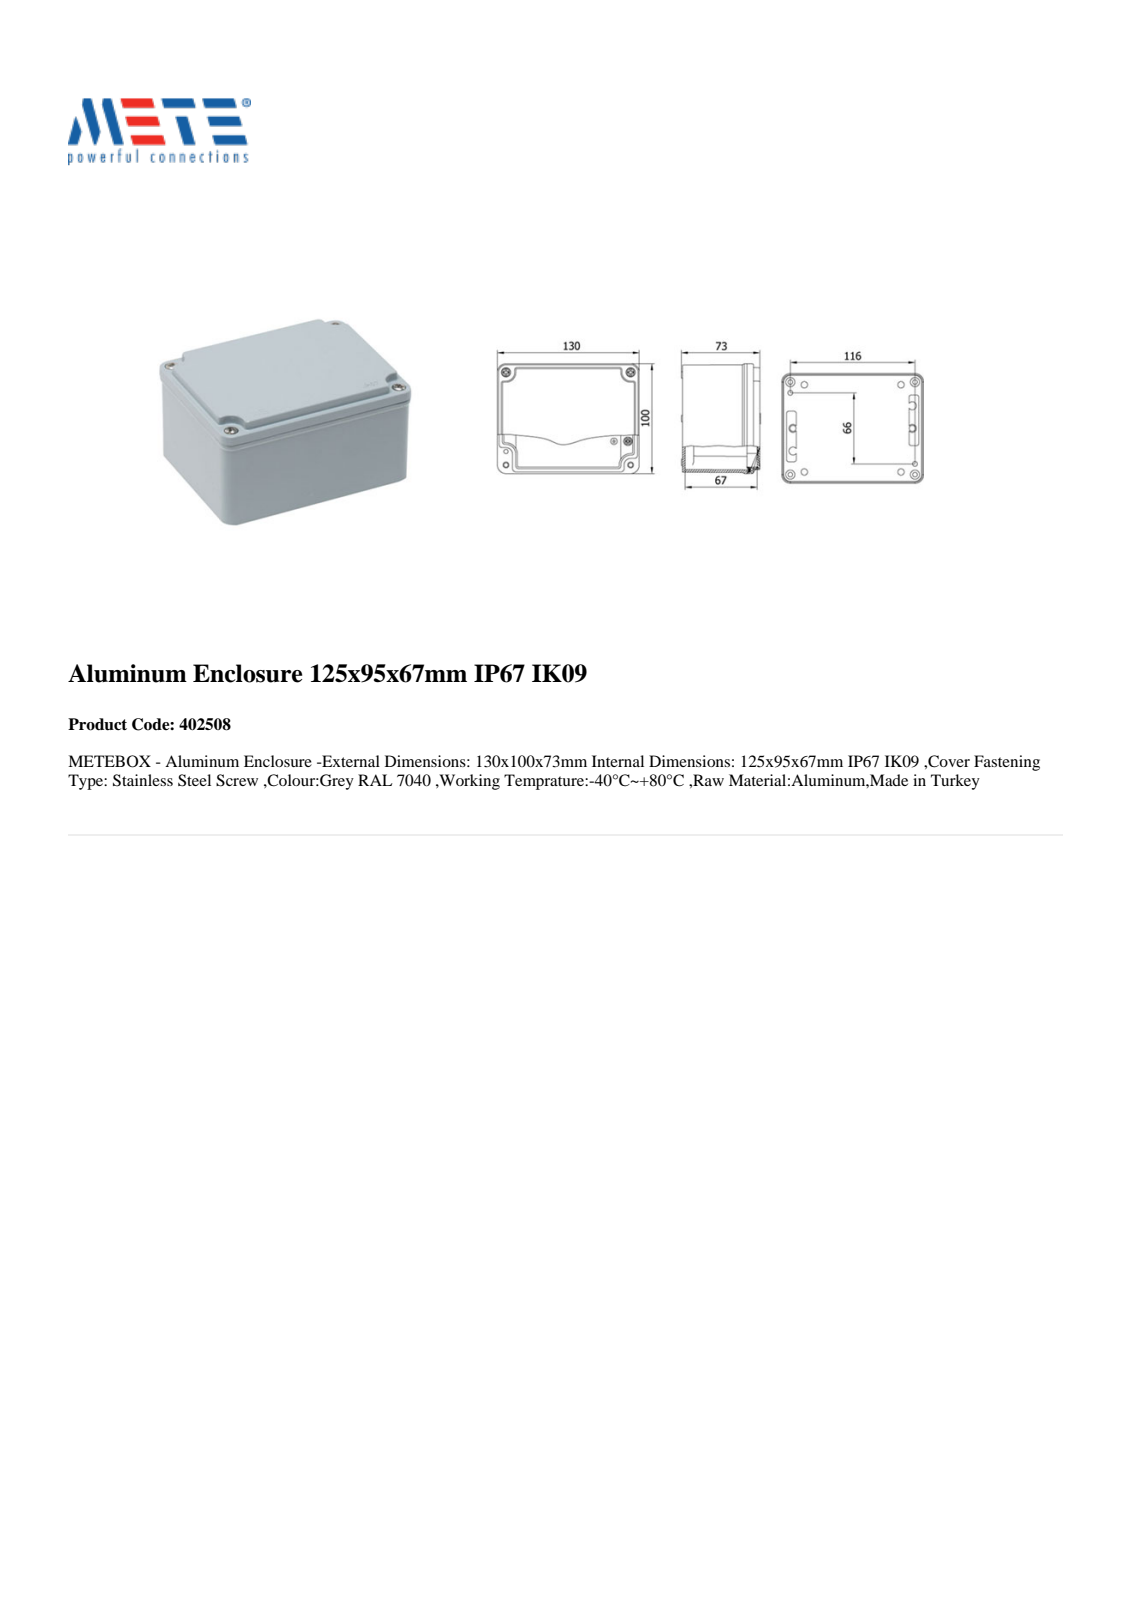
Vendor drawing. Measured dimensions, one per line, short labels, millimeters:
name: mtas17043A55mtlp
written by: SIEMENS PLM Software NX 8.0 (AP203_CONFIGURATION_CONTROLLED_3D_DESIGN_OF_MECHANICAL_PARTS_AND_ASSEMBLIES_MIM_LF)
unit: mm
bodies: 7 solids, 514 faces (211 planar, 147 cylindrical, 156 other)
size: 132 × 102 × 73.5
volume: 207 515 mm³; area: 114 837 mm²
holes: 4× ⌀3.43, 4× ⌀5.5, 2× ⌀3.2, 1× ⌀4, 1× ⌀9
bosses: 6× ⌀6, 4× ⌀4, 1× ⌀8, 1× ⌀3.84, 1× ⌀3.8
rounds: 44× R0.2, 20× R0.1, 12× R0.5, 12× R1, 8× R2, 4× R7
face distances: 2.5, 69.5, 72, 67, 9.5, 60, 57.5, 12, 12.5, 15
hole spacings: 21, 22.14, 43.07, 64.05, 112.97, 115.61, 121.37, 130.3
